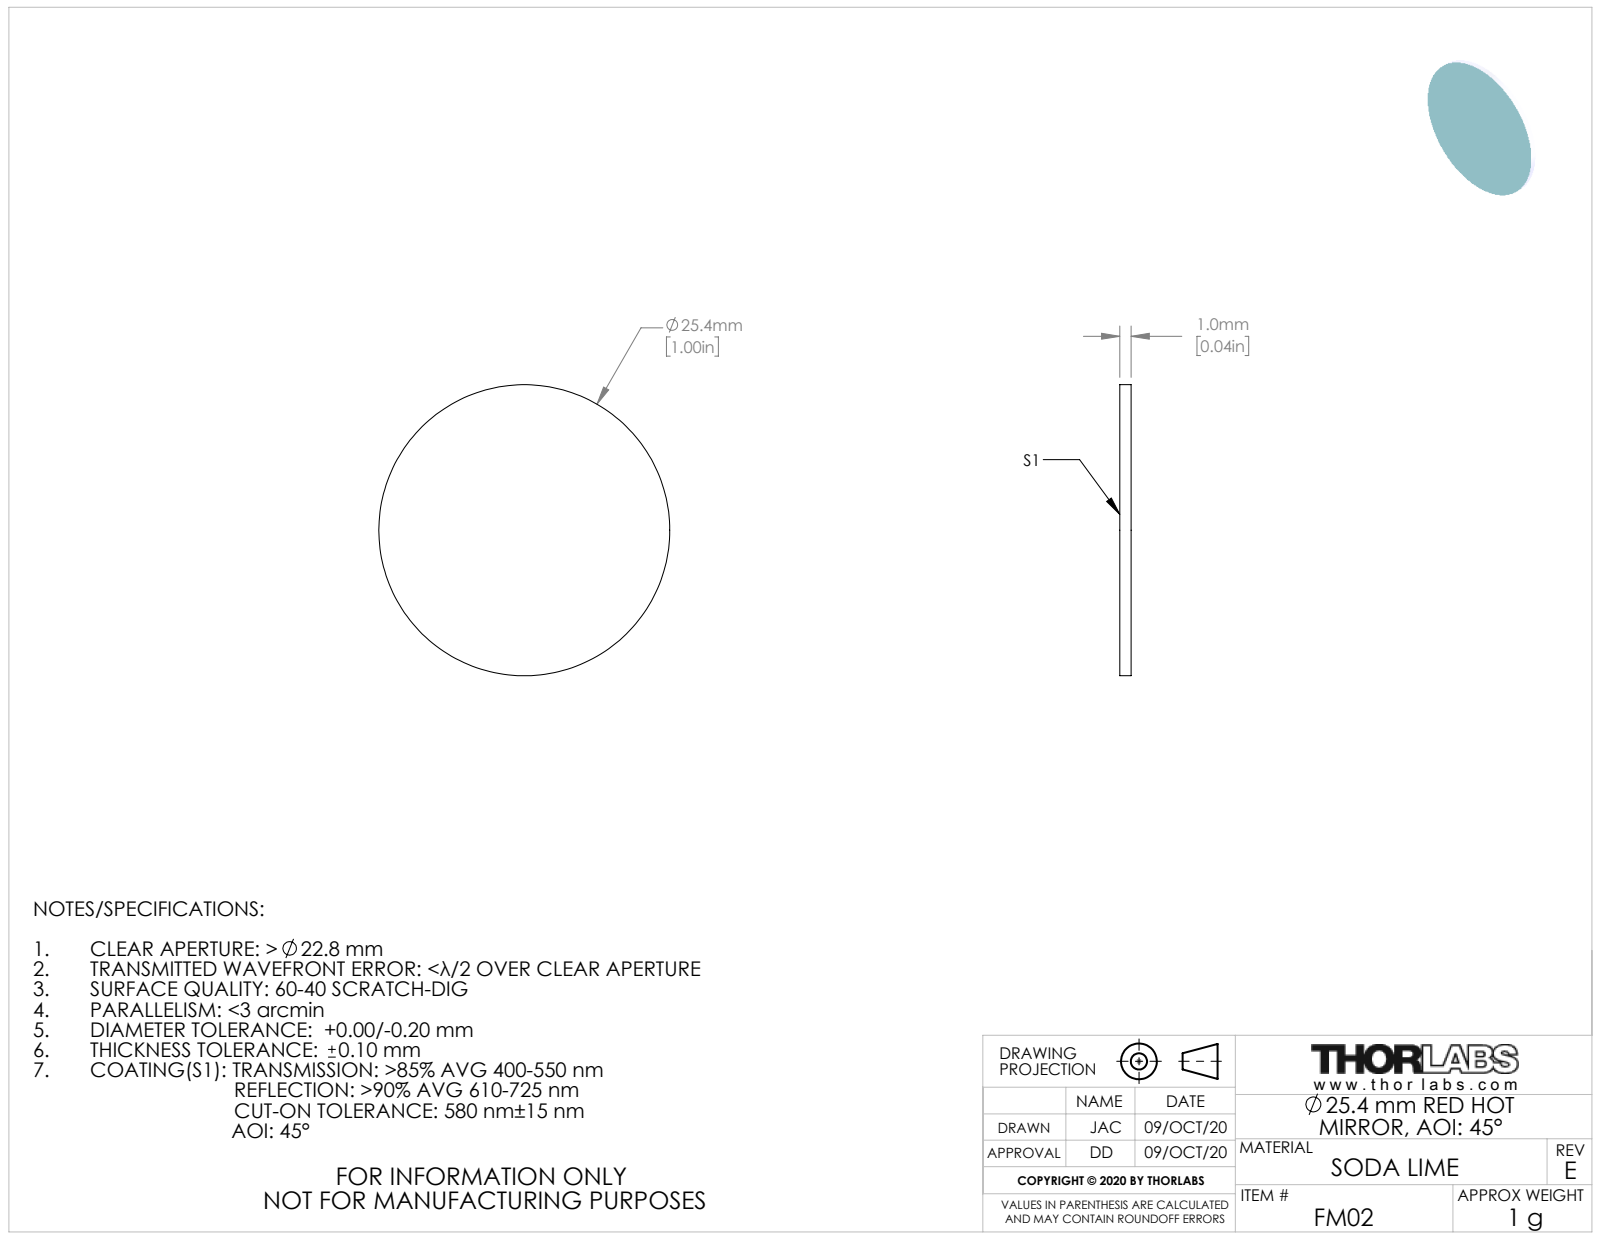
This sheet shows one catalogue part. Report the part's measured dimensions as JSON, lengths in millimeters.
{"part_name": "7279-E0W", "step_written_by": "SolidWorks 2018 (CONFIG_CONTROL_DESIGN)", "units": "millimeters", "bodies": {"solids": 1, "faces": 4, "planar": 2, "cylindrical": 2, "other": 0}, "overall_size": [25.4, 25.4, 1], "volume_mm3": 507, "surface_area_mm2": 1093, "round_bosses_or_shafts": [[25.4, 1]], "face_to_face_distances": [1]}
